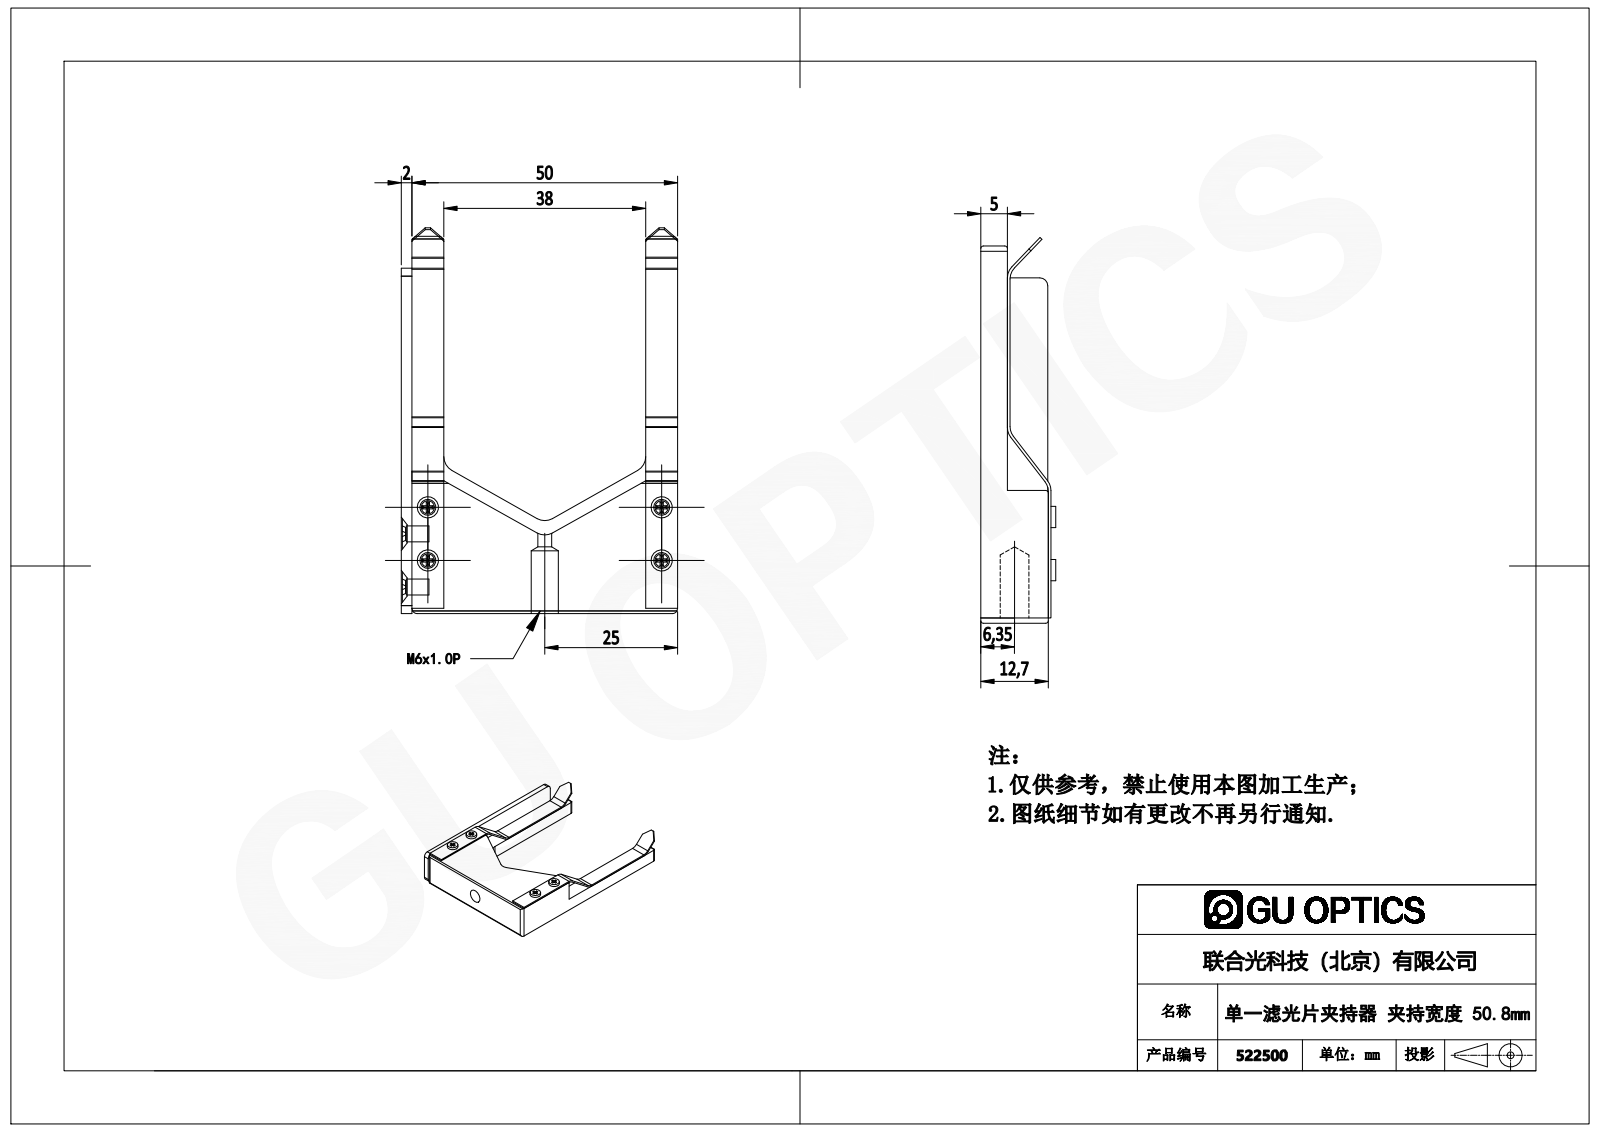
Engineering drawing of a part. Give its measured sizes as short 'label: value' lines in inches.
name: SFH-2
written by: SolidWorks 2012 (CONFIG_CONTROL_DESIGN)
unit: in
bodies: 0 solids, 173 faces (129 planar, 42 cylindrical, 2 other)
size: 2.858 × 2.047 × 0.555
holes: 1× ⌀0.102, 1× ⌀0.201
bosses: 4× ⌀0.157, 2× ⌀0.118
rounds: 10× R0.118, 6× R0.039, 5× R0.02, 4× R0.059
face distances: 0.5, 0.303, 0.02, 0.079, 0.197, 2.047, 1.969, 0.236, 1.732, 0.283
